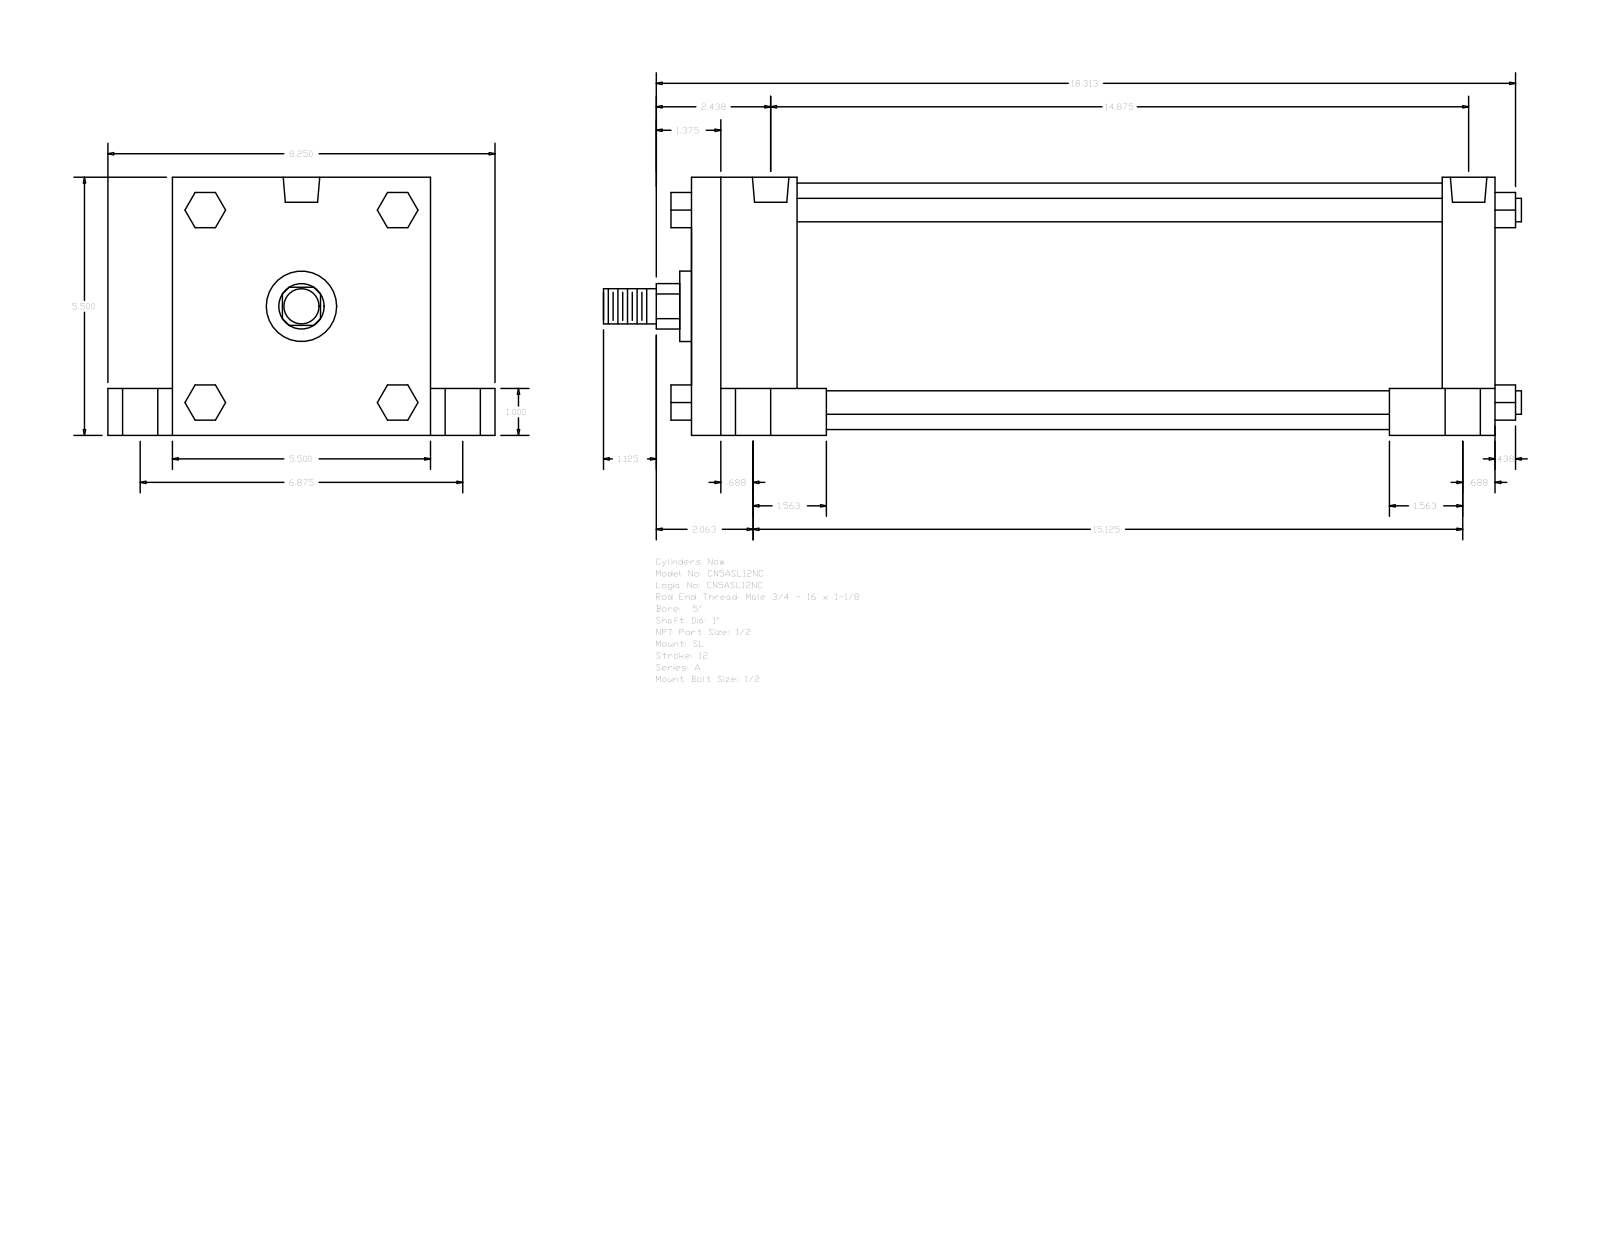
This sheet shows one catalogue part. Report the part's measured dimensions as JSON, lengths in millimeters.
{"part_name": "A_SL__0500_1", "step_written_by": "GSSL Pune (CONFIG_CONTROL_DESIGN)", "units": "millimeters", "bodies": {"solids": 0, "faces": 150, "planar": 114, "cylindrical": 36, "other": 0}, "overall_size": [496.89, 209.55, 139.7], "round_holes": [[8.73, 4], [19.05, 4], [25.4, 4], [19.77, 2]], "round_bosses_or_shafts": [[12.7, 4], [133.35, 1], [38.1, 1], [25.4, 1], [19.05, 1]], "partial_cylinders_radius": [[12.29, 1]], "face_to_face_distances": [139.7, 434.97, 28.57, 25.4, 114.3, 34.93, 174.63, 57.15, 406.4, 349.25], "hole_center_spacings": [2.39, 87.31, 87.37, 87.83, 88.12, 174.62, 373.05, 375.44]}
